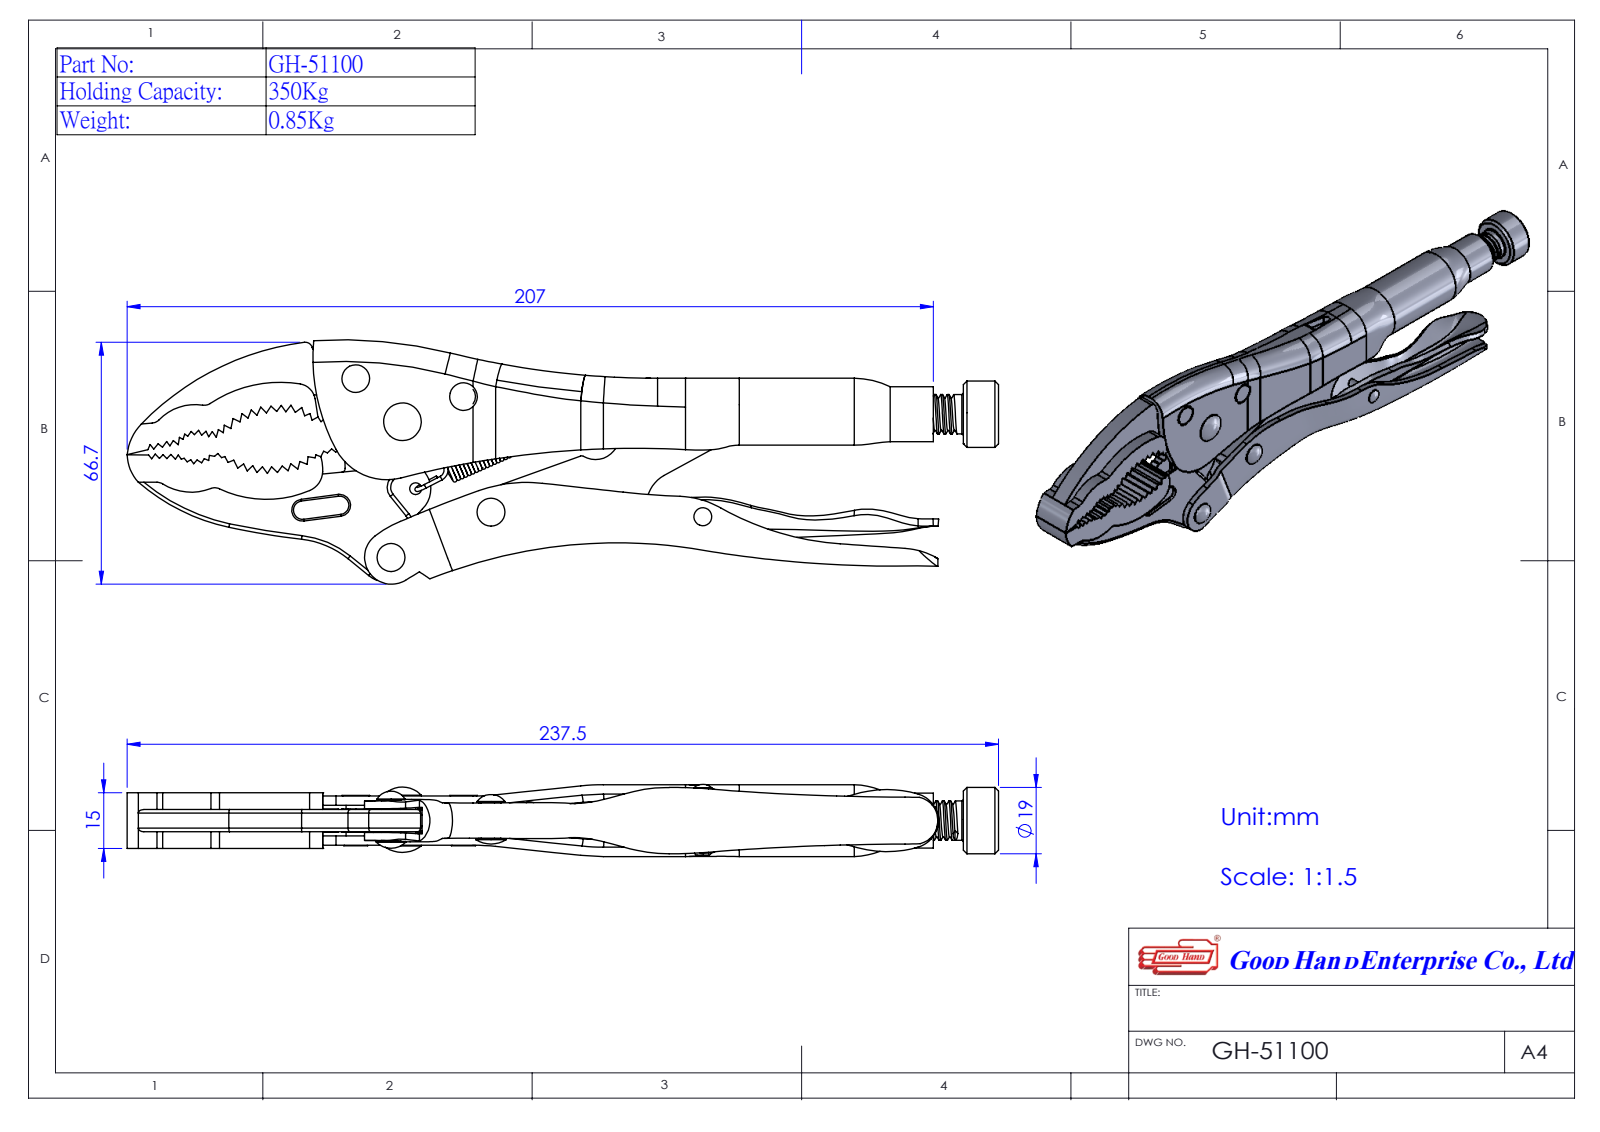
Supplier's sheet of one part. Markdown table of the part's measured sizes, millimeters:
| quantity | value |
| --- | --- |
| part name | GH-51100(單一零件); Group1^GH-51100(單一零件) |
| STEP written by | SolidWorks 2016 (AUTOMOTIVE_DESIGN) |
| units | millimeters |
| bodies | 3 solids, 629 faces (211 planar, 270 cylindrical, 148 other) |
| overall size | 241.85 × 68.01 × 20.1 |
| volume | 79 734 mm³ |
| surface area | 55 546 mm² |
| round holes (diameter × count) | 11.81 × 1, 14.8 × 1 |
| round bosses / shafts (diameter × count) | 1.2 × 3, 7.8 × 2, 5.4 × 2, 5.35 × 2, 20 × 1, 18.5 × 1, 15.3 × 1, 11 × 1 |
| partial cylindrical surfaces (radius × count) | 1 × 14, 3 × 5, 60 × 4, 2 × 3, 0.5 × 2, 1.5 × 2, 4 × 2, 10 × 2 |
| main face-to-face distances | 4.55, 0.9, 10.05, 2.6, 5.4, 0.8, 1.15, 1.95, 6.55, 7.35 |
